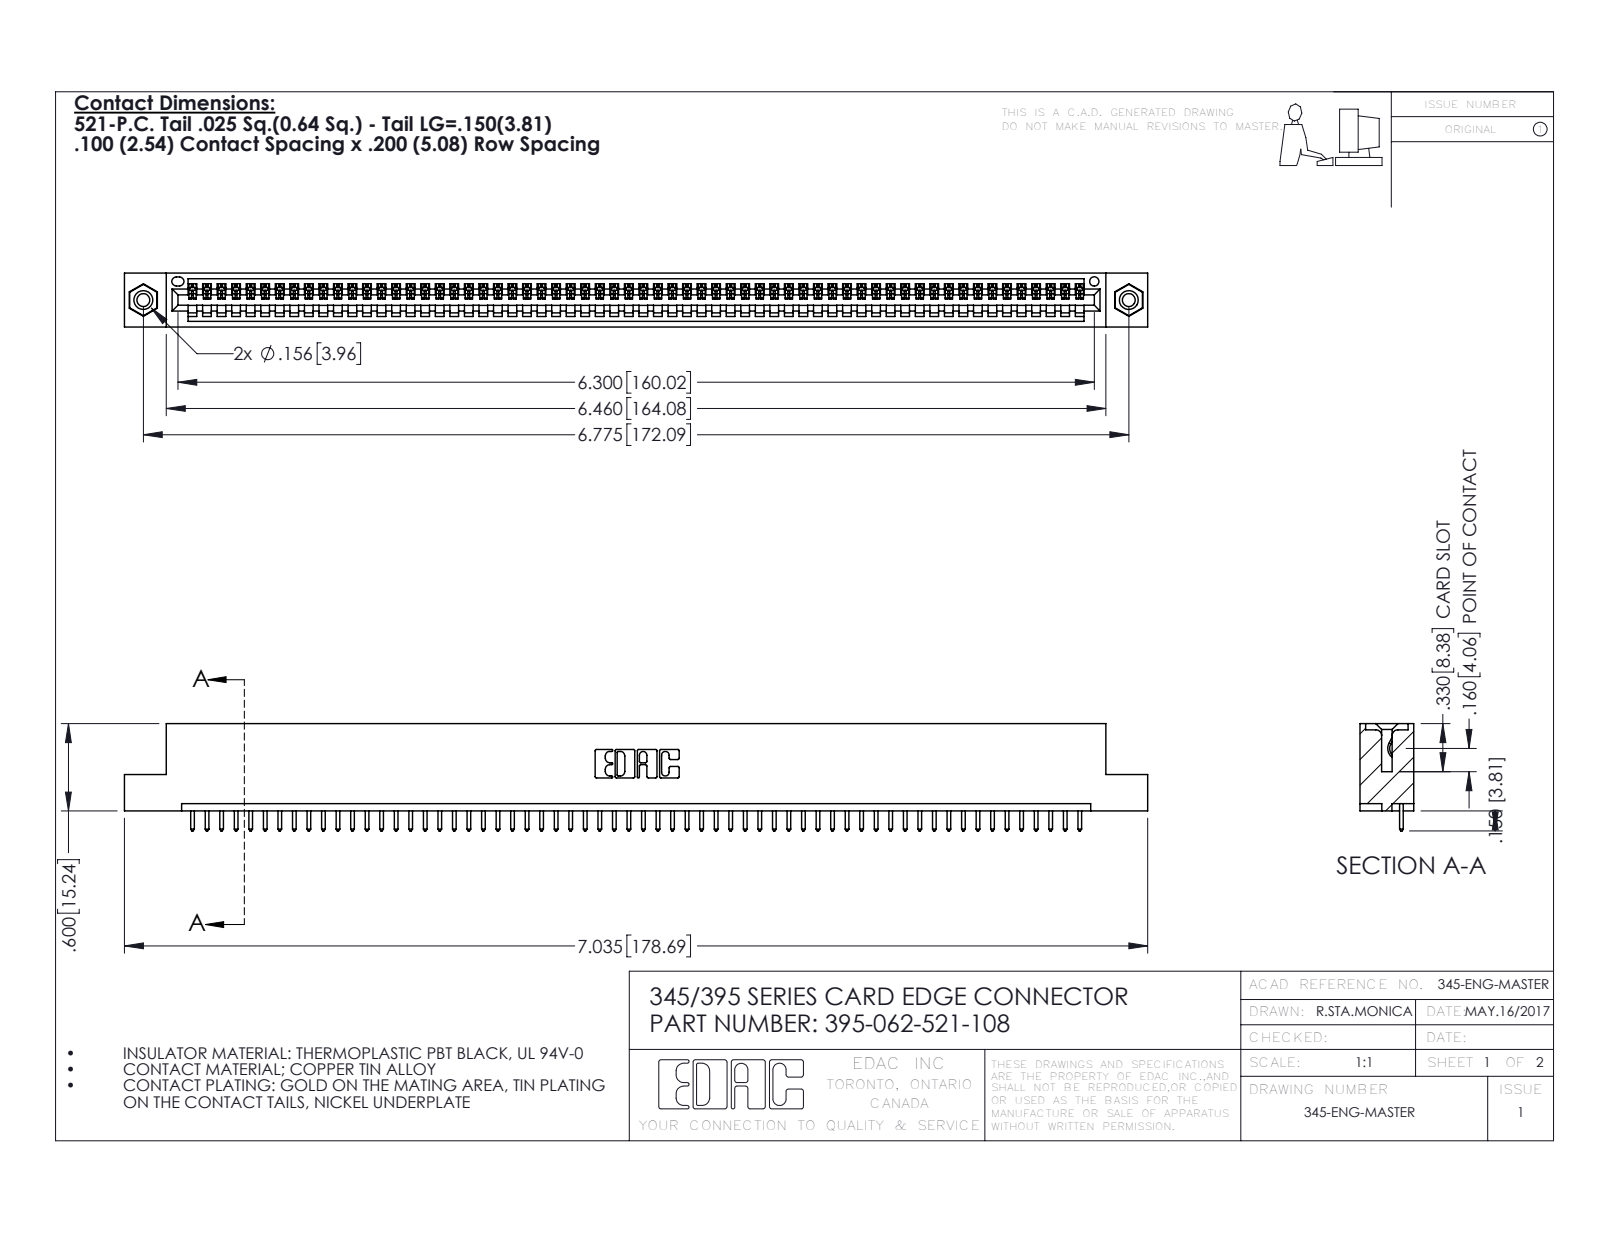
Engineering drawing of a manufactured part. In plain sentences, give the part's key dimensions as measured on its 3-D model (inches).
The part is named "345-250-001_345-250-003-102; 395-062-521-108; 345-292-001_345-293-121; 345 Part_Flush Mounting Lugs - 0.156 Dia-TI". Its 3-D file was written by "SolidWorks 2016 (CONFIG_CONTROL_DESIGN)". It is 65 solids with 3782 faces: 2592 planar, 1174 cylindrical and 16 other. Overall it measures 7.035 by 0.737 by 0.37 inches. Its volume is 1.035 cubic inches and its surface area 34.3 square inches. Round holes: 2 of diameter 0.089, 2 of diameter 0.125, 2 of diameter 0.156, 1 of diameter 0.064. Round bosses or shafts: 2 of diameter 0.155. Partial cylindrical surfaces (rounded edges, fillets, slot ends): 124 of radius 0.006, 124 of radius 0.01, 22 of radius 0.01, 6 of radius 0.007, 6 of radius 0.031, 3 of radius 0.026, 2 of radius 0.031, 2 of radius 0.04. The main face-to-face distances are 0.072, 0.298, 0.37, 0.2, 0.098, 0.272, 0.025, 0.225, 0.149, 0.072. The hole center spacings are 0.27, 6.539, 6.775.
